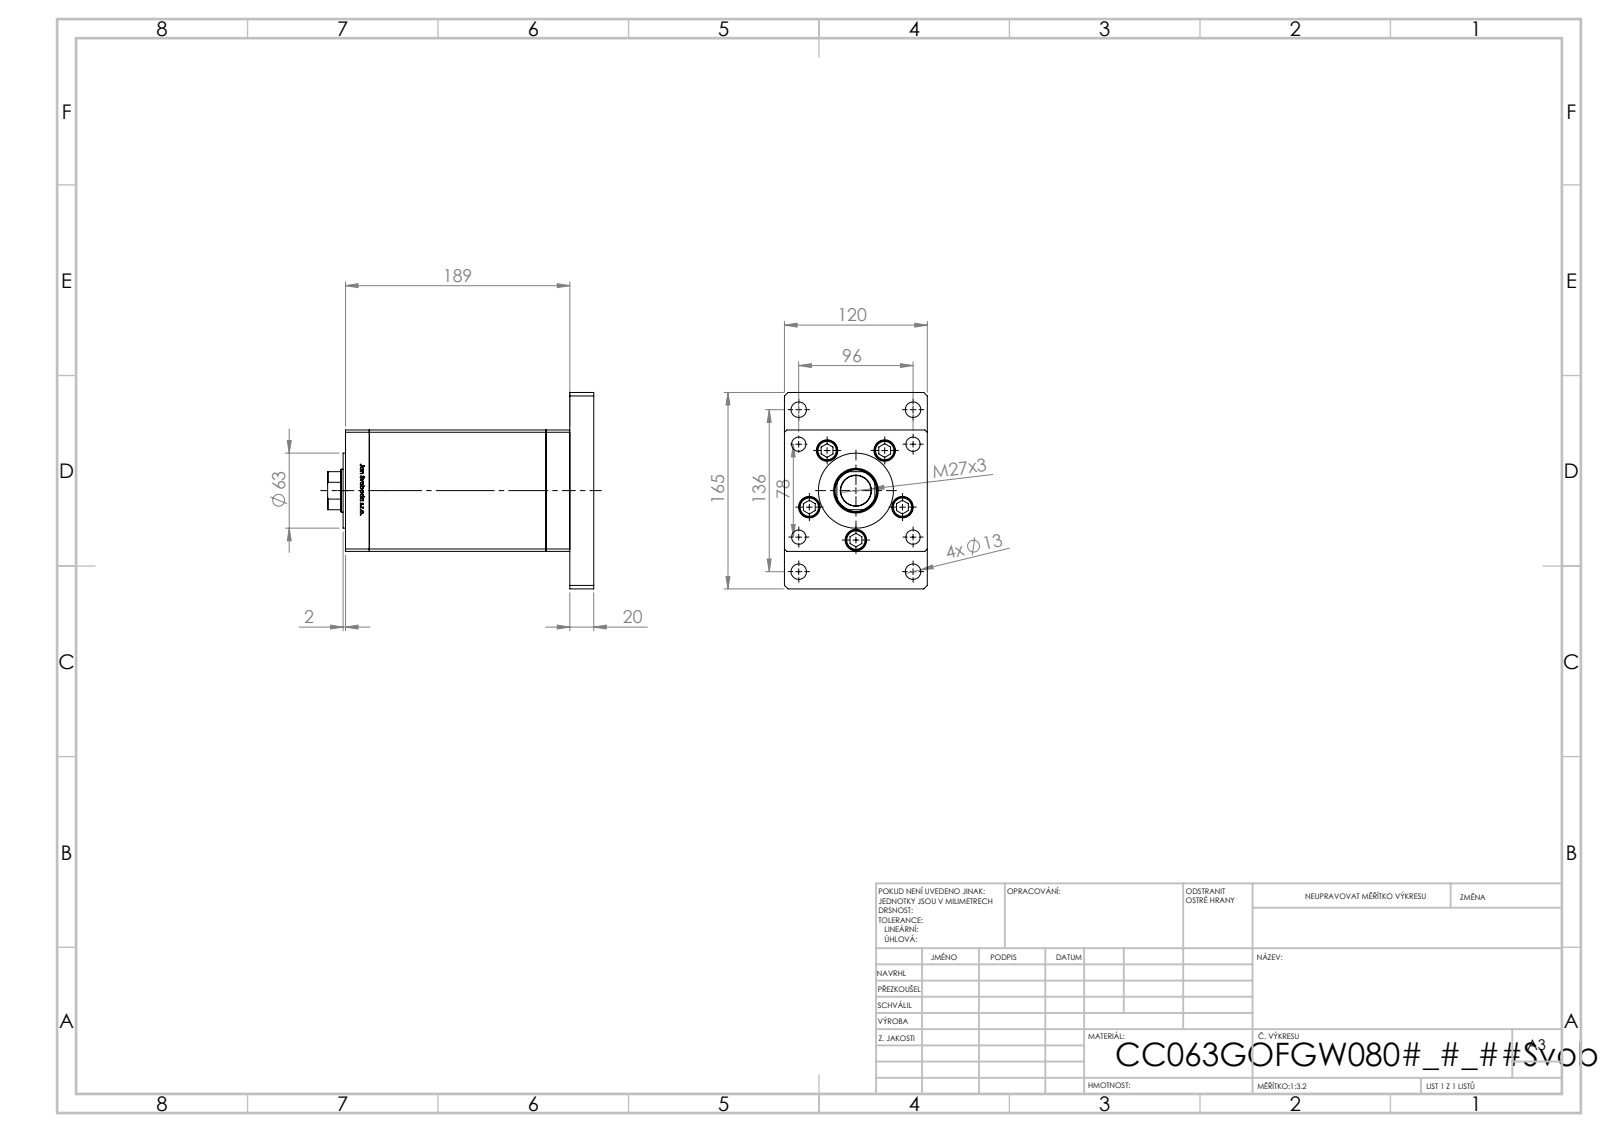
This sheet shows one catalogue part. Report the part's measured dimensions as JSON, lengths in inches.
{"part_name": "V220C_FRONT_G; V220C_F; ALLEN BOLT; V220C_G_MIDDLE (+2 more)", "step_written_by": "SolidWorks 2019 (CONFIG_CONTROL_DESIGN)", "units": "inches", "bodies": {"solids": 19, "faces": 1301, "planar": 514, "cylindrical": 181, "other": 606}, "overall_size": [8.799, 6.496, 4.724], "volume_in3": 146.3, "surface_area_in2": 491.6, "round_holes": [[0.472, 9], [0.531, 5], [0.709, 5], [0.512, 4], [0.669, 4], [1.004, 1], [1.417, 1], [1.476, 1], [3.268, 1]], "round_bosses_or_shafts": [[0.315, 9], [0.669, 5], [2.48, 1]], "partial_cylinders_radius": [[0.037, 2], [0.689, 1]], "face_to_face_distances": [0.787, 6.634, 4.724, 7.421, 4.016, 5.846, 1.575, 0.079, 7.343, 0.709], "hole_center_spacings": [1.634, 1.142, 2.435, 3.277, 3.78, 3.948, 4.213, 5.659]}
